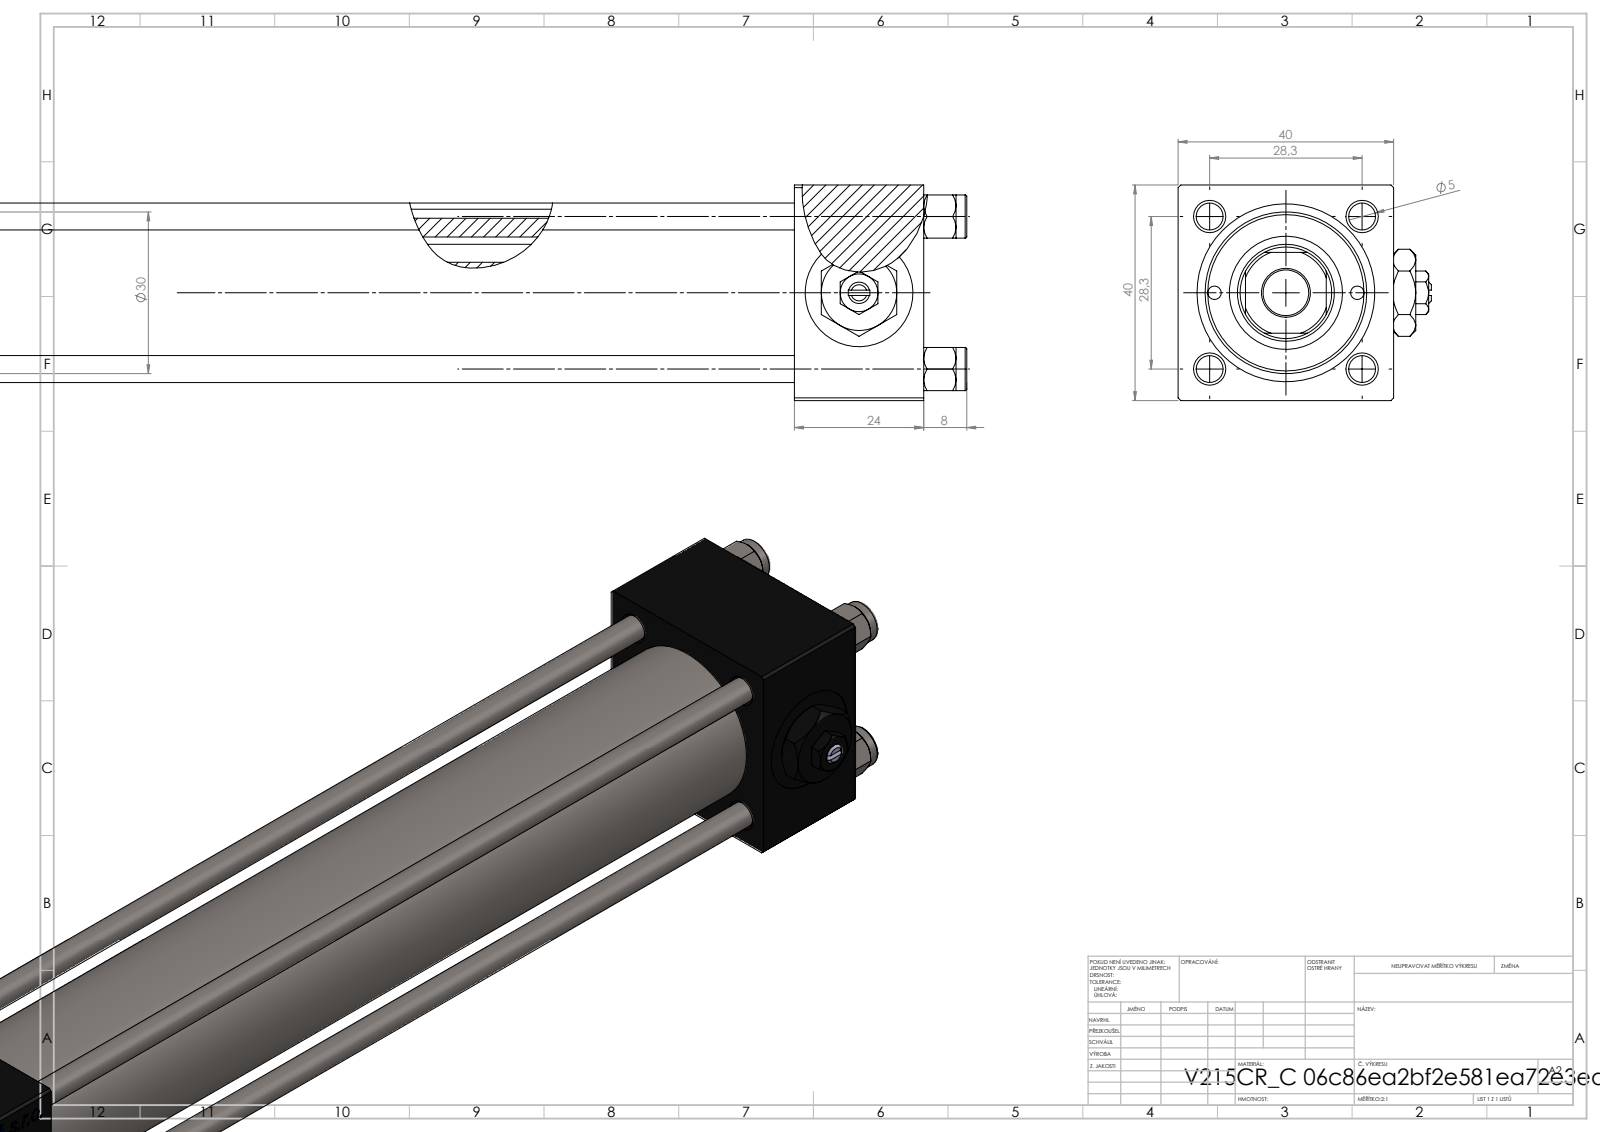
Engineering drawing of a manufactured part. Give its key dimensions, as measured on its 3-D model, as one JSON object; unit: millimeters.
{"part_name": "Zatka_pro_OIL_PORT; NUT_M5_C; V215_VC_A; V215CR_C_Body (+2 more)", "step_written_by": "SolidWorks 2019 (CONFIG_CONTROL_DESIGN)", "units": "millimeters", "bodies": {"solids": 13, "faces": 1251, "planar": 573, "cylindrical": 100, "other": 578}, "overall_size": [282, 47, 40], "volume_mm3": 232041, "surface_area_mm2": 100016, "round_holes": [[5, 4], [20, 3], [2.5, 2], [7, 2], [13.16, 2], [8.5, 1], [18, 1], [21, 1], [25, 1], [30, 1]], "round_bosses_or_shafts": [[8, 4], [31, 1]], "partial_cylinders_radius": [[8.5, 1]], "face_to_face_distances": [40, 24, 39.8, 211, 187, 230.3, 206.3, 19.3, 48, 235], "hole_center_spacings": [14.18, 20.01, 28.3, 30.84, 13.25, 40.02, 26.5, 212]}
